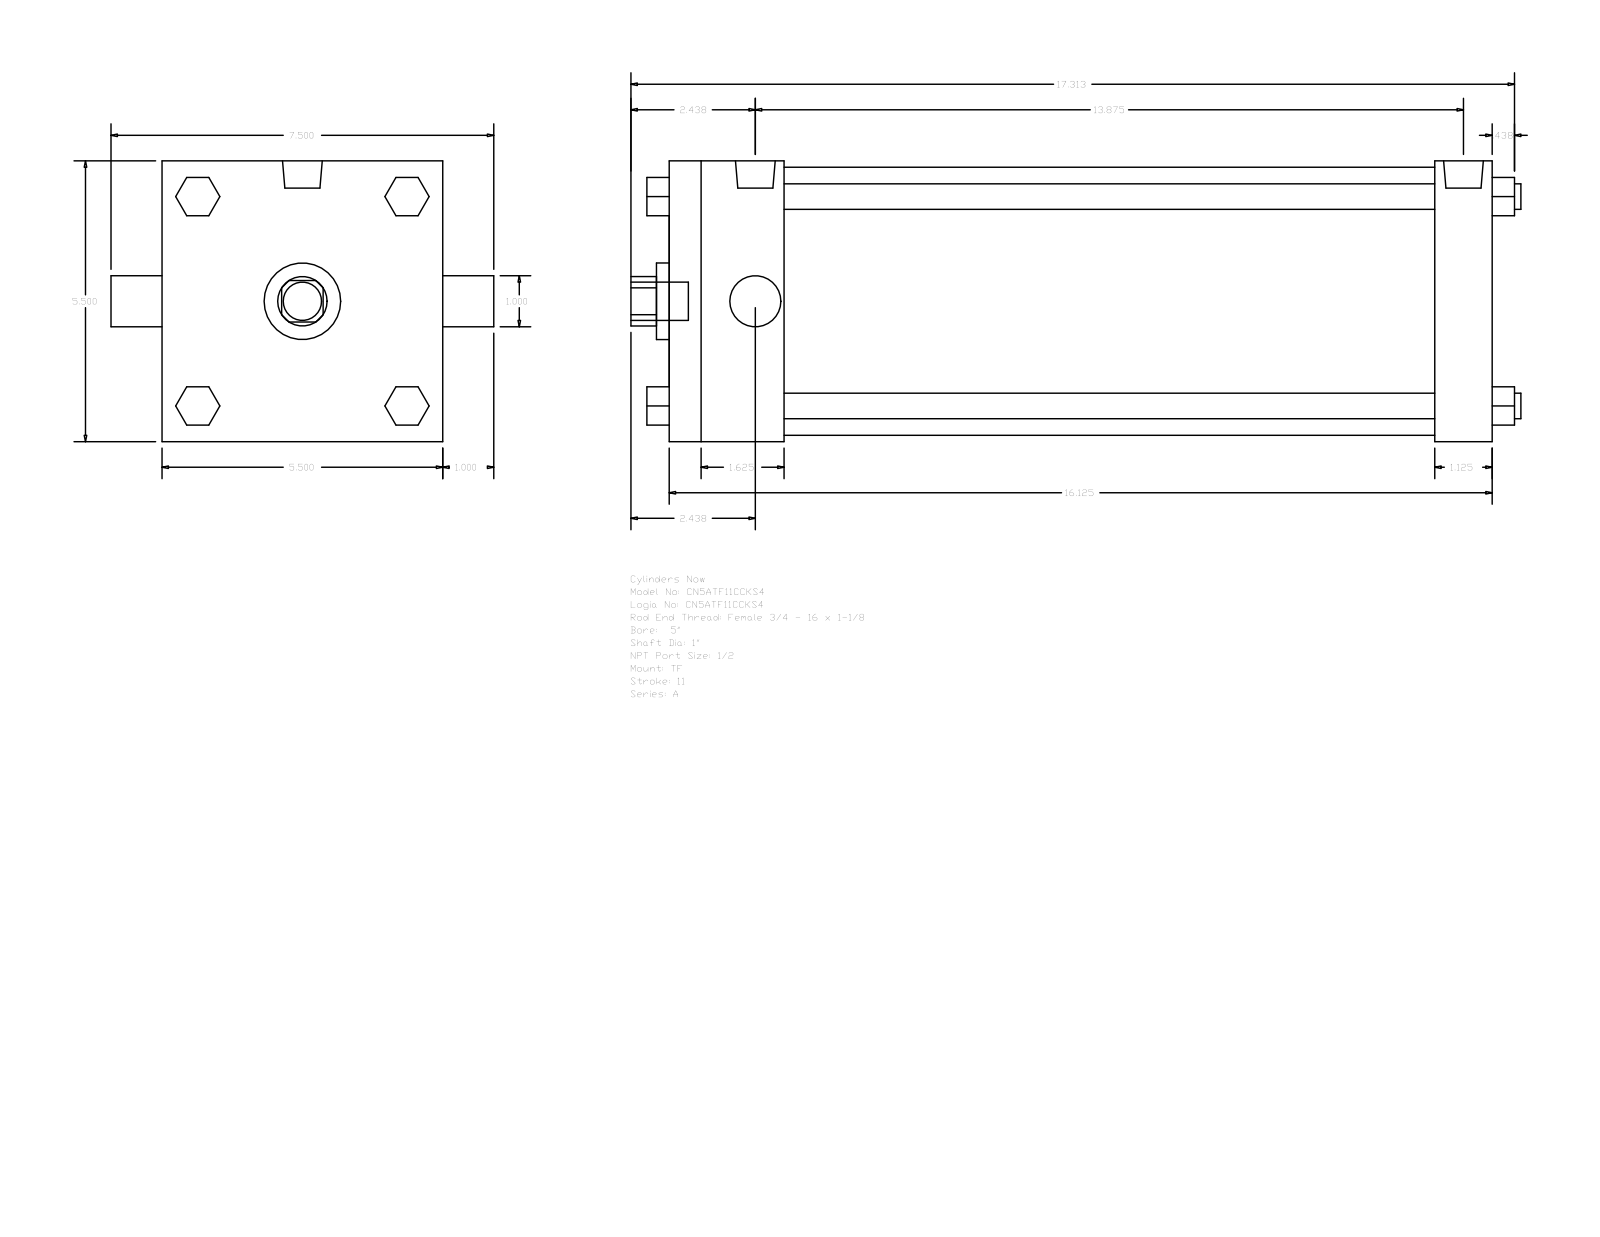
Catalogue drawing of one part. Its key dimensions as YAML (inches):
part_name: "A_TF__0500_1"
step_written_by: "GSSL Pune (CONFIG_CONTROL_DESIGN)"
units: inches
bodies: {solids: 0, faces: 120, planar: 92, cylindrical: 28, other: 0}
overall_size: [17.437, 7.5, 5.5]
round_holes:
  - {diameter: 1, count: 2}
  - {diameter: 1.5, count: 1}
  - {diameter: 5.25, count: 1}
round_bosses_or_shafts:
  - {diameter: 0.5, count: 4}
  - {diameter: 0.344, count: 3}
  - {diameter: 0.778, count: 2}
  - {diameter: 0.75, count: 1}
partial_cylinders:
  - {radius: 0.484, count: 1}
face_to_face_distances: [5.5, 16.125, 1.125, 15, 2.25, 12.75, 13.875, 0.75, 2.05, 3.55]
